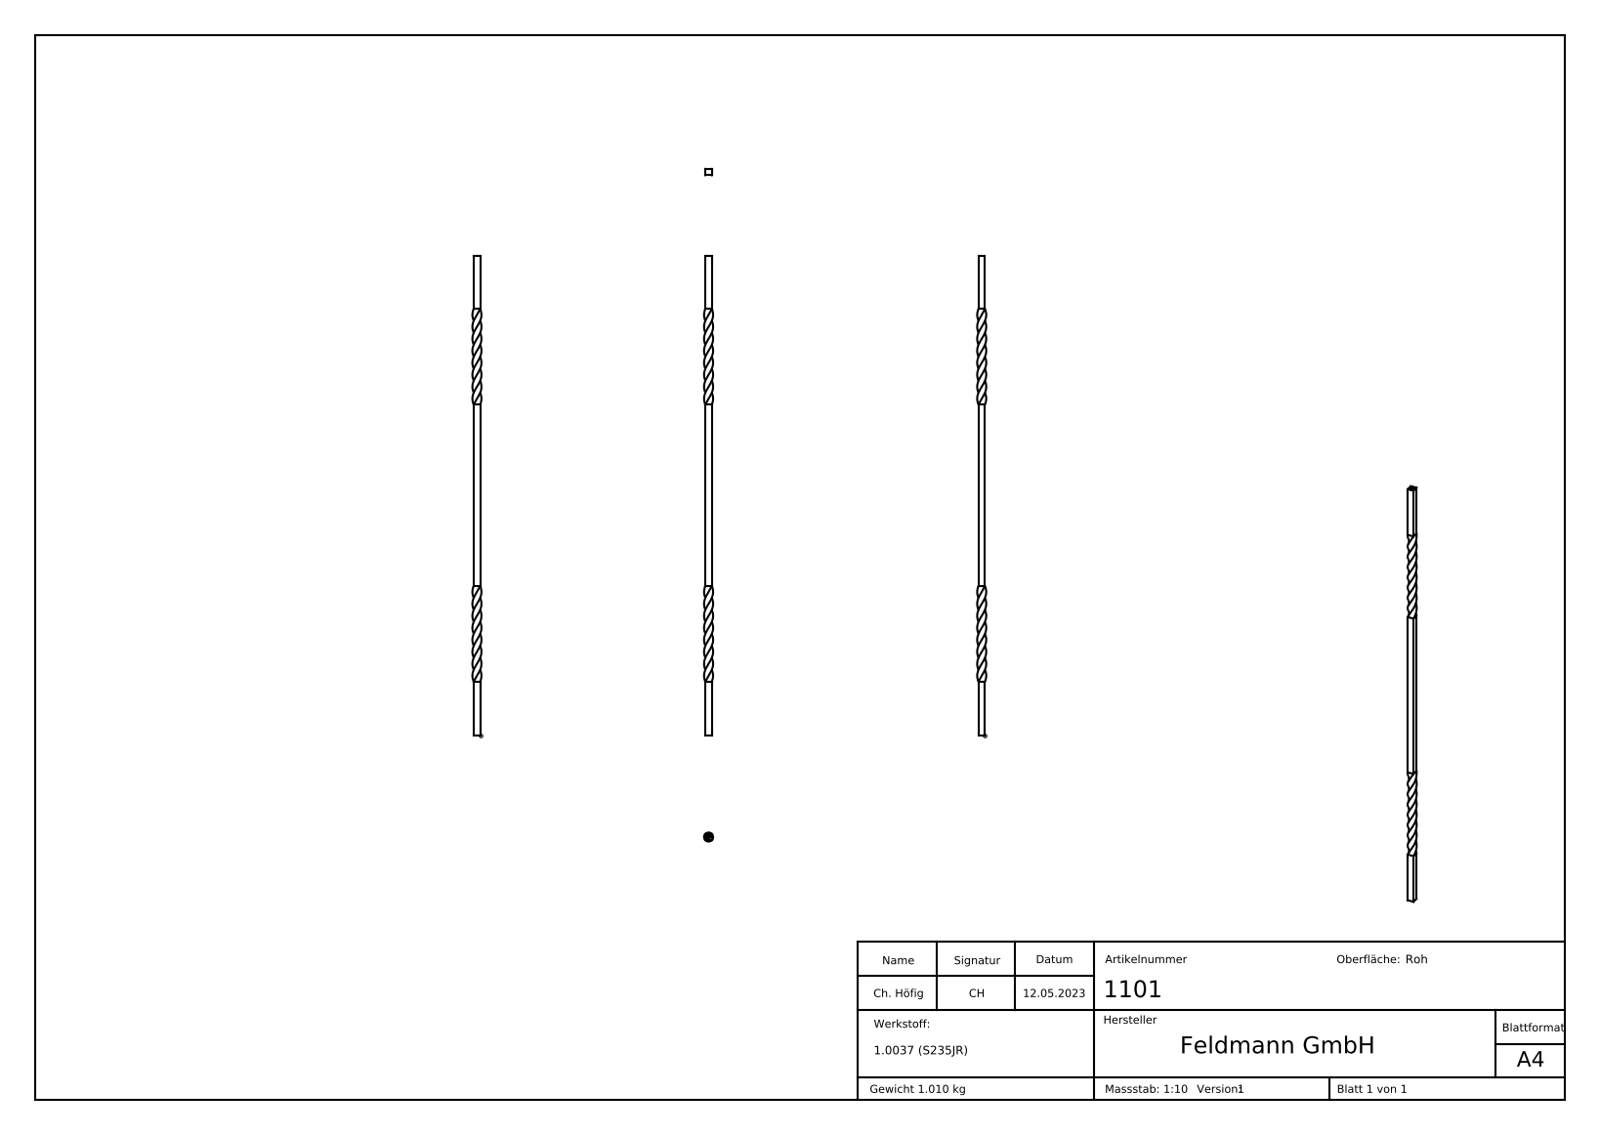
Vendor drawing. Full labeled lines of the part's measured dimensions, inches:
Part name (STEP PRODUCT): 1101
STEP written by: SolidWorks 2018 (CONFIG_CONTROL_DESIGN)
Units: inches
Bodies: 1 solid, 210 faces (125 planar, 0 cylindrical, 85 other)
Overall size (bounding box): 35.433 × 0.67 × 0.67
Volume: 7.902 in³ · Surface area: 68.16 in²
Main face-to-face distances: 0.472, 35.433, 35.429, 0.022, 0.147, 0.018, 0.027, 0.045, 0.112, 0.106
